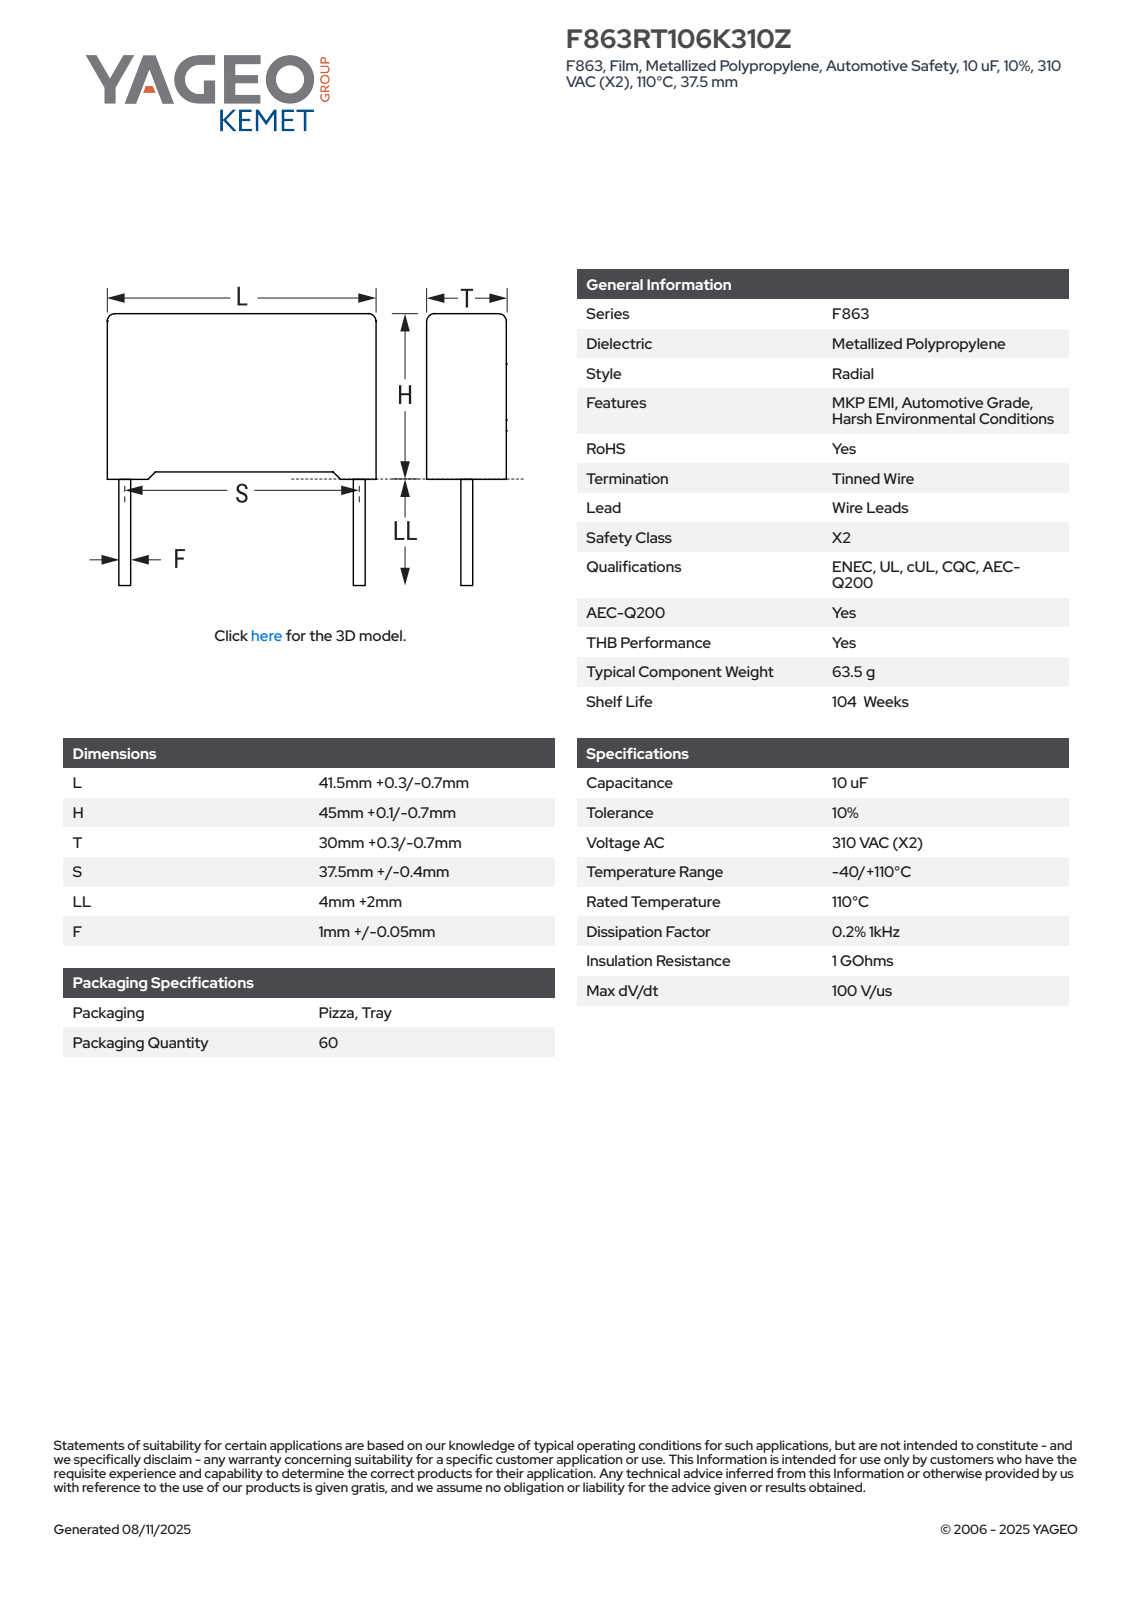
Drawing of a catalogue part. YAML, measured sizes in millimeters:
part_name: "CFR_RB_41.5X45X30_L41.8H45.1T30.3S37.5LL6F1.05"
step_written_by: "SolidWorks 2014 (AUTOMOTIVE_DESIGN)"
units: millimeters
bodies: {solids: 4, faces: 89, planar: 81, cylindrical: 8, other: 0}
overall_size: [51.1, 41.8, 30.3]
volume: 54511
surface_area: 8916
round_bosses_or_shafts:
  - {diameter: 1.05, count: 2}
partial_cylinders:
  - {radius: 1.62, count: 4}
face_to_face_distances: [30.3, 41.8, 43.07, 30.31, 0.6, 29.7, 0.61, 29.1, 29.71, 2.03]
